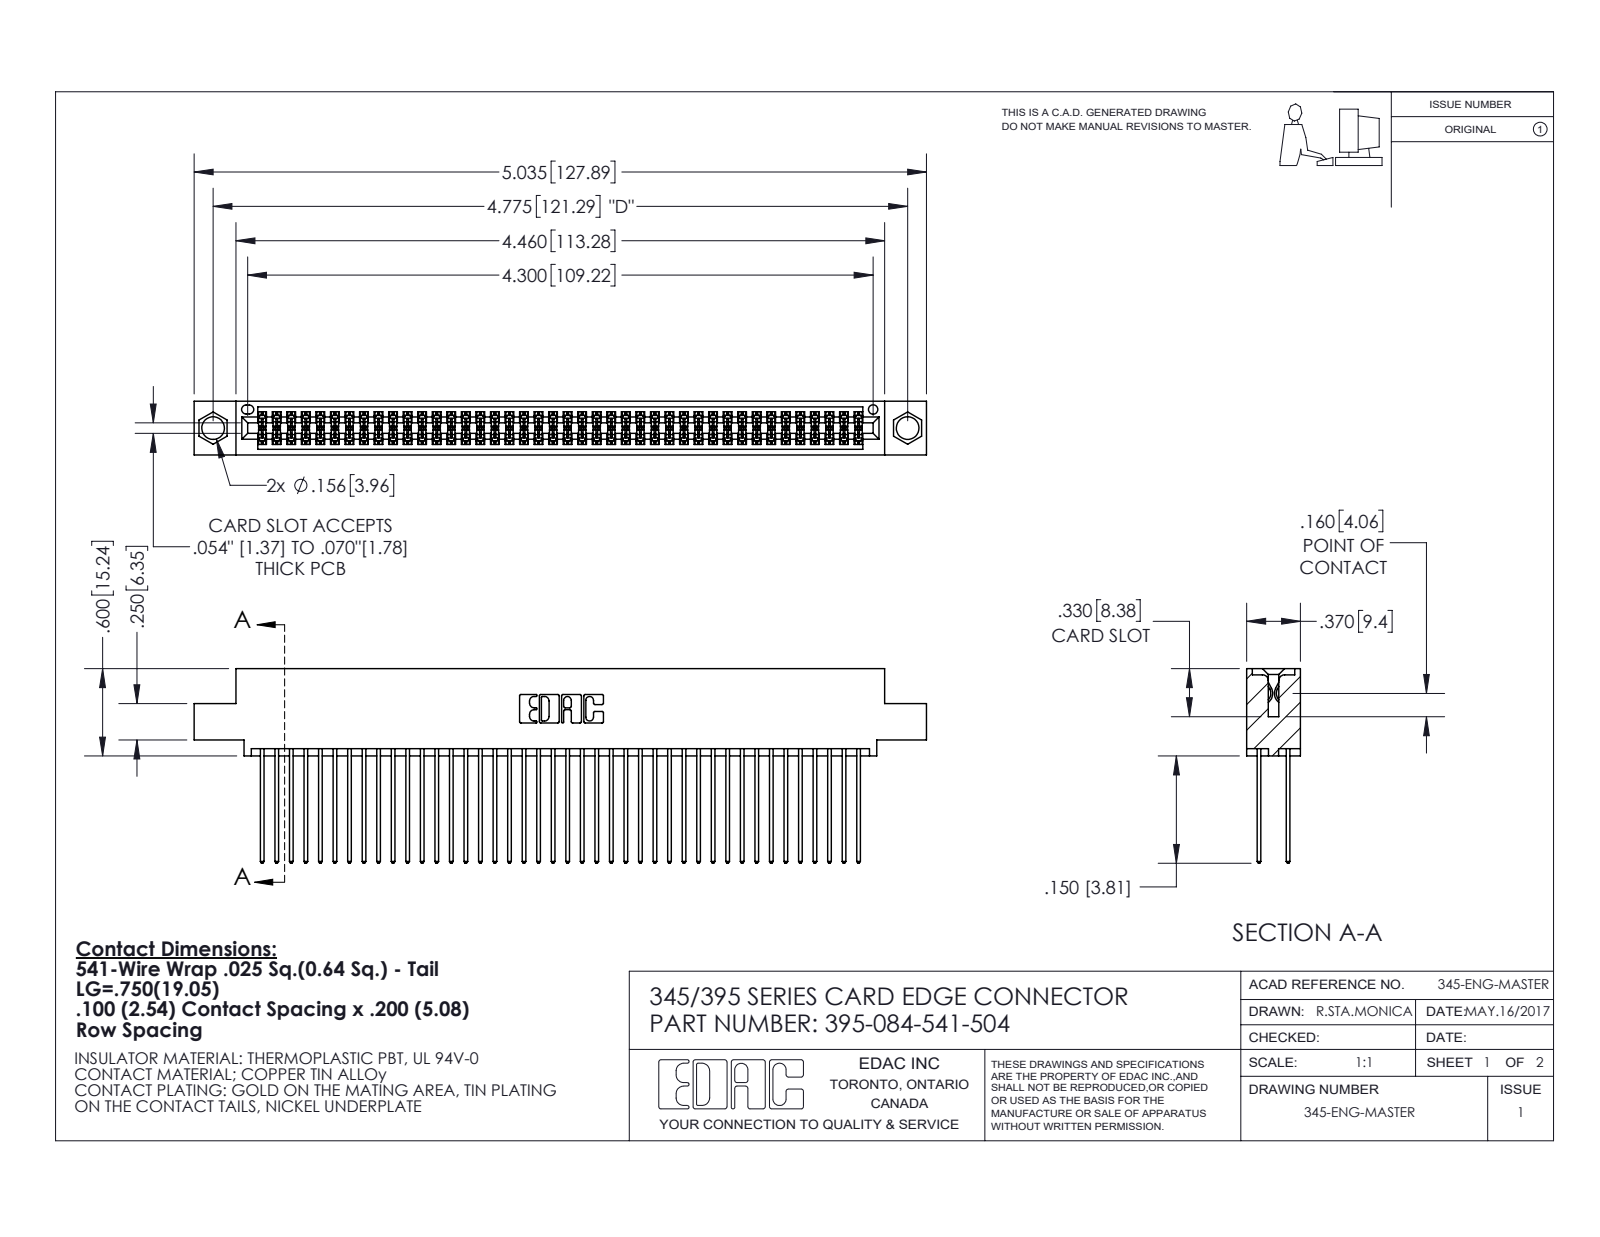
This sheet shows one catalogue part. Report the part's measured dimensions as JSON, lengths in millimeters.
{"part_name": "395-084-541-504; 345-292-001_345-293-141; 345 Part_0.110 Offset - 0.156 Dia-TI", "step_written_by": "SolidWorks 2020 (CONFIG_CONTROL_DESIGN)", "units": "millimeters", "bodies": {"solids": 85, "faces": 4344, "planar": 2870, "cylindrical": 1474, "other": 0}, "overall_size": [127.9, 34, 9.4], "volume_mm3": 12700, "surface_area_mm2": 21020, "round_holes": [[4, 2], [1.6, 1]], "partial_cylinders_radius": [[0.2, 126], [0.3, 84], [0.3, 22], [0.2, 6], [0.8, 6], [0.7, 3], [0.4, 2], [0.5, 2]], "face_to_face_distances": [1.8, 7.6, 5.1, 2.5, 6.9, 0.6, 5.7, 9.4, 4.4, 3.8], "hole_center_spacings": [6.9, 115.3, 121.3]}
